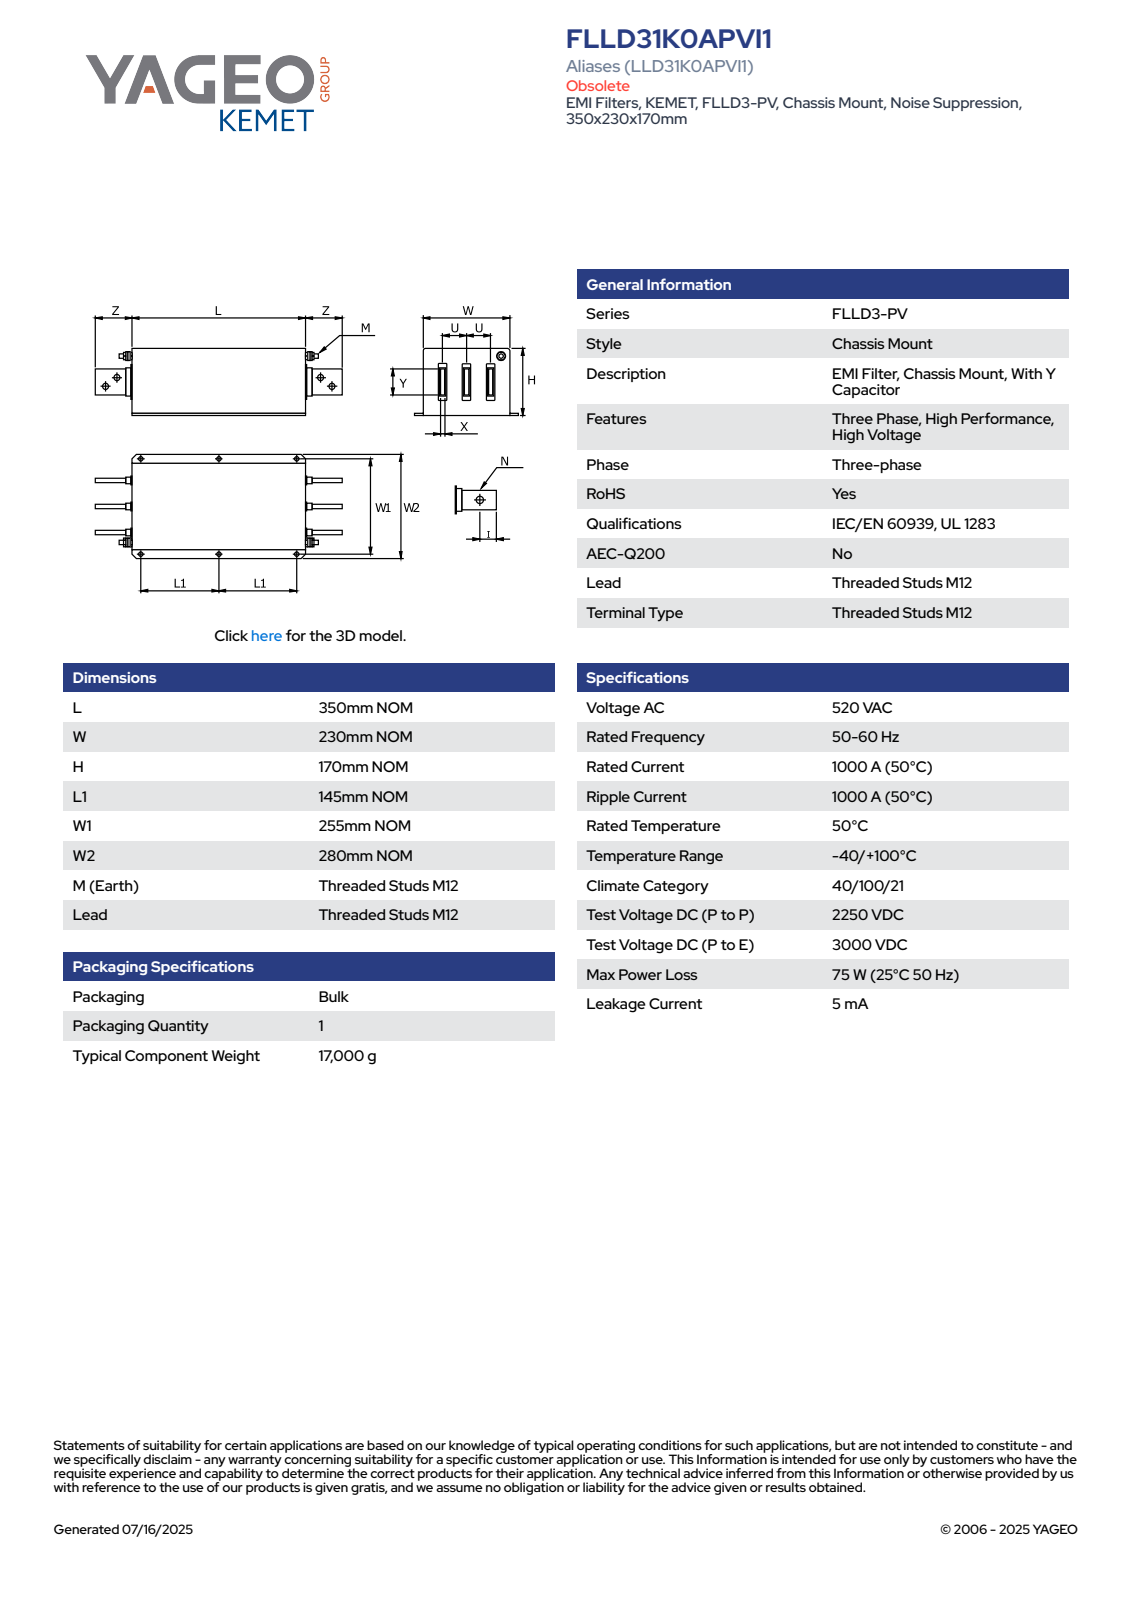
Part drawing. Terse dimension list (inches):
name: WASHER M12 Ø24_93475A290; HEX NUT M12x1.75_90592A028; FLLD31K0APVI1_EXT; Tank bush M4 (+8 more)
written by: SolidWorks 2021 (AUTOMOTIVE_DESIGN)
unit: in
bodies: 84 solids, 3058 faces (734 planar, 962 cylindrical, 1362 other)
size: 18.11 × 11.024 × 6.693
volume: 54.85 in³; area: 1 465 in²
holes: 19× ⌀0.071, 15× ⌀0.134, 10× ⌀0.126, 6× ⌀0.472, 4× ⌀0.197, 4× ⌀0.205, 3× ⌀0.551, 1× ⌀0.512
bosses: 13× ⌀0.126, 4× ⌀0.276, 1× ⌀0.945, 1× ⌀0.472
rounds: 84× R0.079, 64× R0.02, 36× R0.008, 30× R0.039, 24× R0.01, 10× R0.098, 4× R0.059, 2× R0.118
face distances: 0.079, 0.039, 8.976, 6.614, 13.701, 6.654, 6.693, 6.575, 13.622, 8.898
hole spacings: 2.362, 3.63, 5.038, 5.709, 7.932, 11.549, 12.87, 2.756
